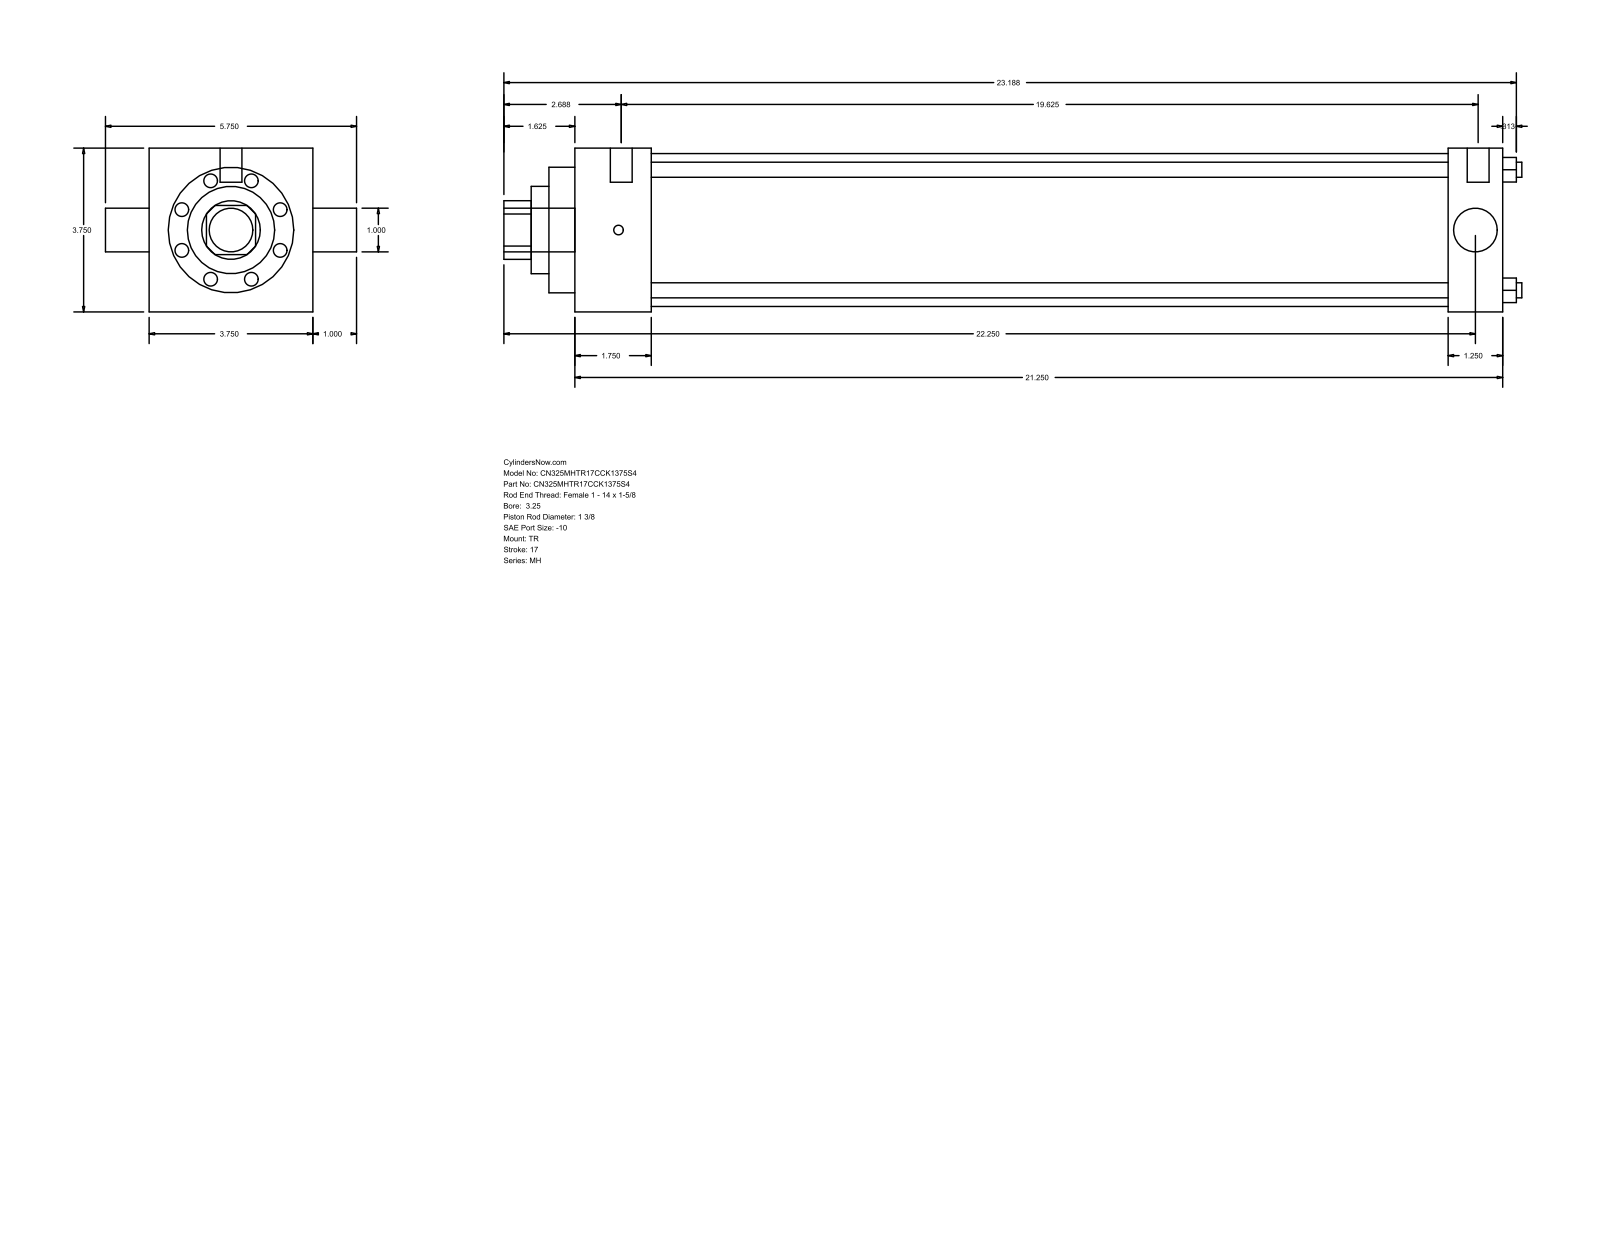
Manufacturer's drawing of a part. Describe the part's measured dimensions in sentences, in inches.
The part is named "MH_TR__0325_1.375". Its 3-D file was written by "GSSL Pune (CONFIG_CONTROL_DESIGN)". It is 0 solids with 86 faces: 61 planar, 25 cylindrical and 0 other. Overall it measures 23.313 by 5.75 by 3.75 inches. Round holes: 4 of diameter 0.345, 1 of diameter 1, 1 of diameter 1.375, 1 of diameter 2, 1 of diameter 2.875, 1 of diameter 3.5. Round bosses or shafts: 3 of diameter 0.219, 2 of diameter 0.5, 1 of diameter 1. Partial cylindrical surfaces (rounded edges, fillets, slot ends): 1 of radius 0.672. The main face-to-face distances are 3.75, 21.25, 1.75, 20, 18.25, 19.5, 1.25, 0.594, 2.344, 20.594. The hole center spacings are 1.952, 2.76, 3.903.
